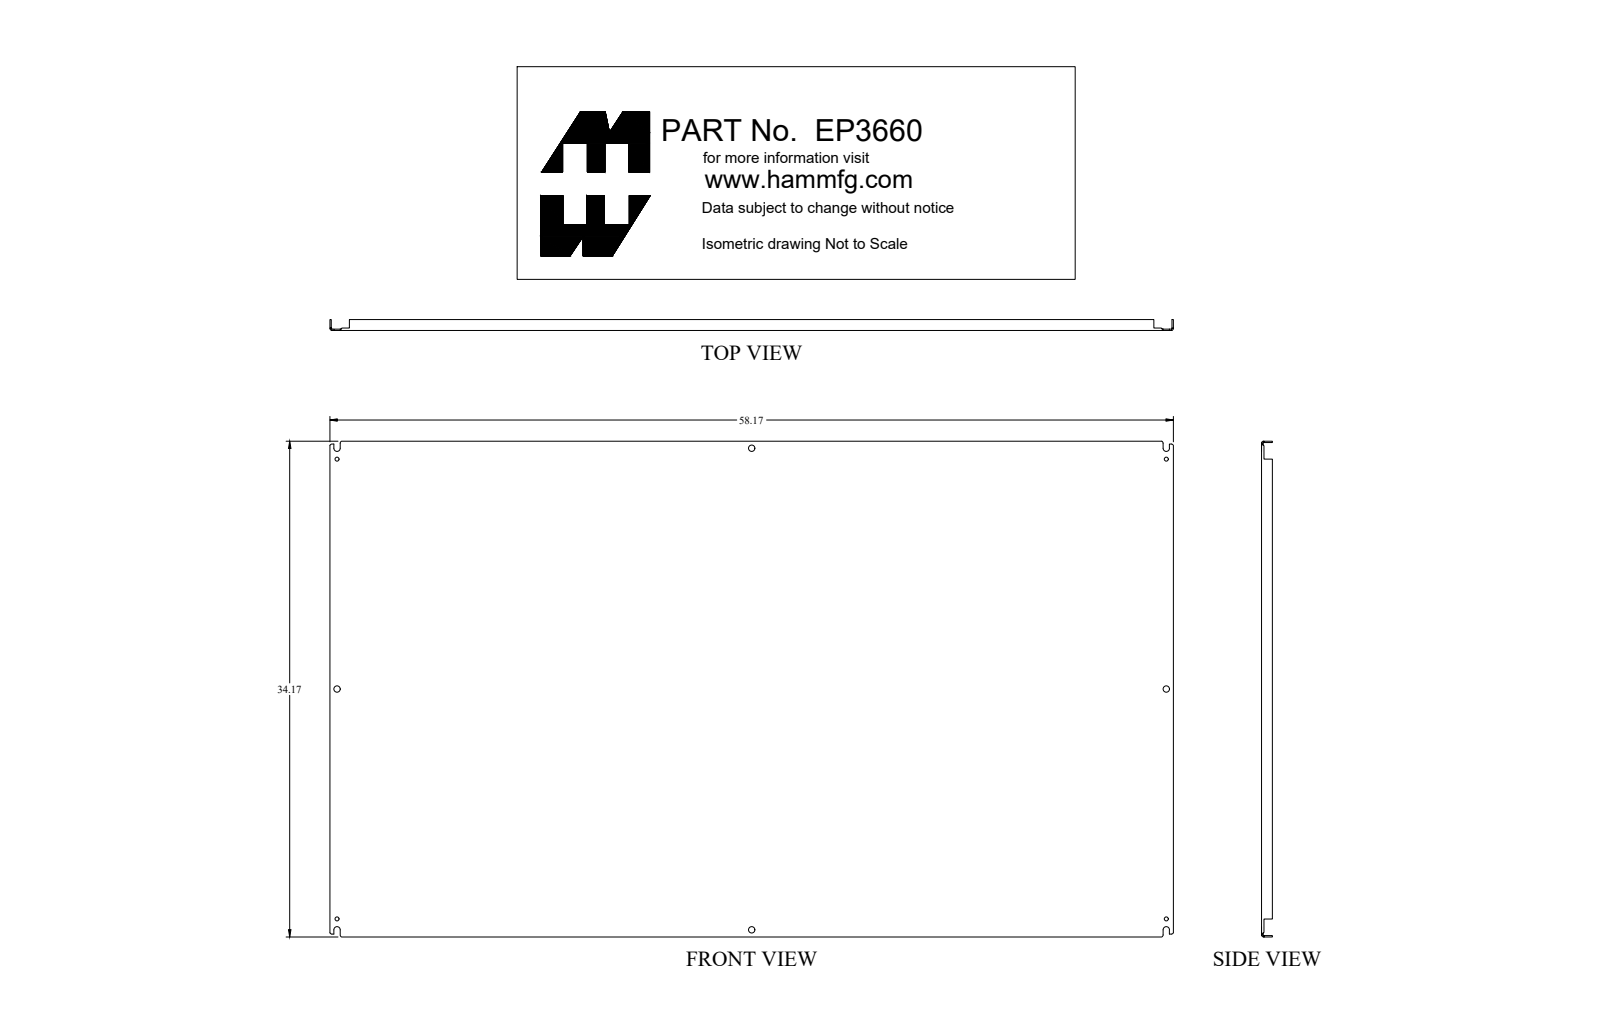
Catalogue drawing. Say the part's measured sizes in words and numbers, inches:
The part is named "EP3660". Its 3-D file was written by "SolidWorks 2018 (AUTOMOTIVE_DESIGN)". It is 1 solid with 136 faces: 74 planar, 46 cylindrical and 16 other. Overall it measures 58.17 by 34.17 by 0.75 inches. Its volume is 198.8 cubic inches and its surface area 4 204 square inches. Round holes: 4 of diameter 0.281, 4 of diameter 0.437. Partial cylindrical surfaces (rounded edges, fillets, slot ends): 4 of radius 0.048, 4 of radius 0.063, 4 of radius 0.143, 4 of radius 0.219. The main face-to-face distances are 0.095, 34.075, 58.075, 34.17, 33.98, 58.17, 57.98, 0.75, 0.655, 0.171. The hole center spacings are 15.844, 28.604, 33.06, 43.242, 59.343, 57.188, 31.688, 65.381.
